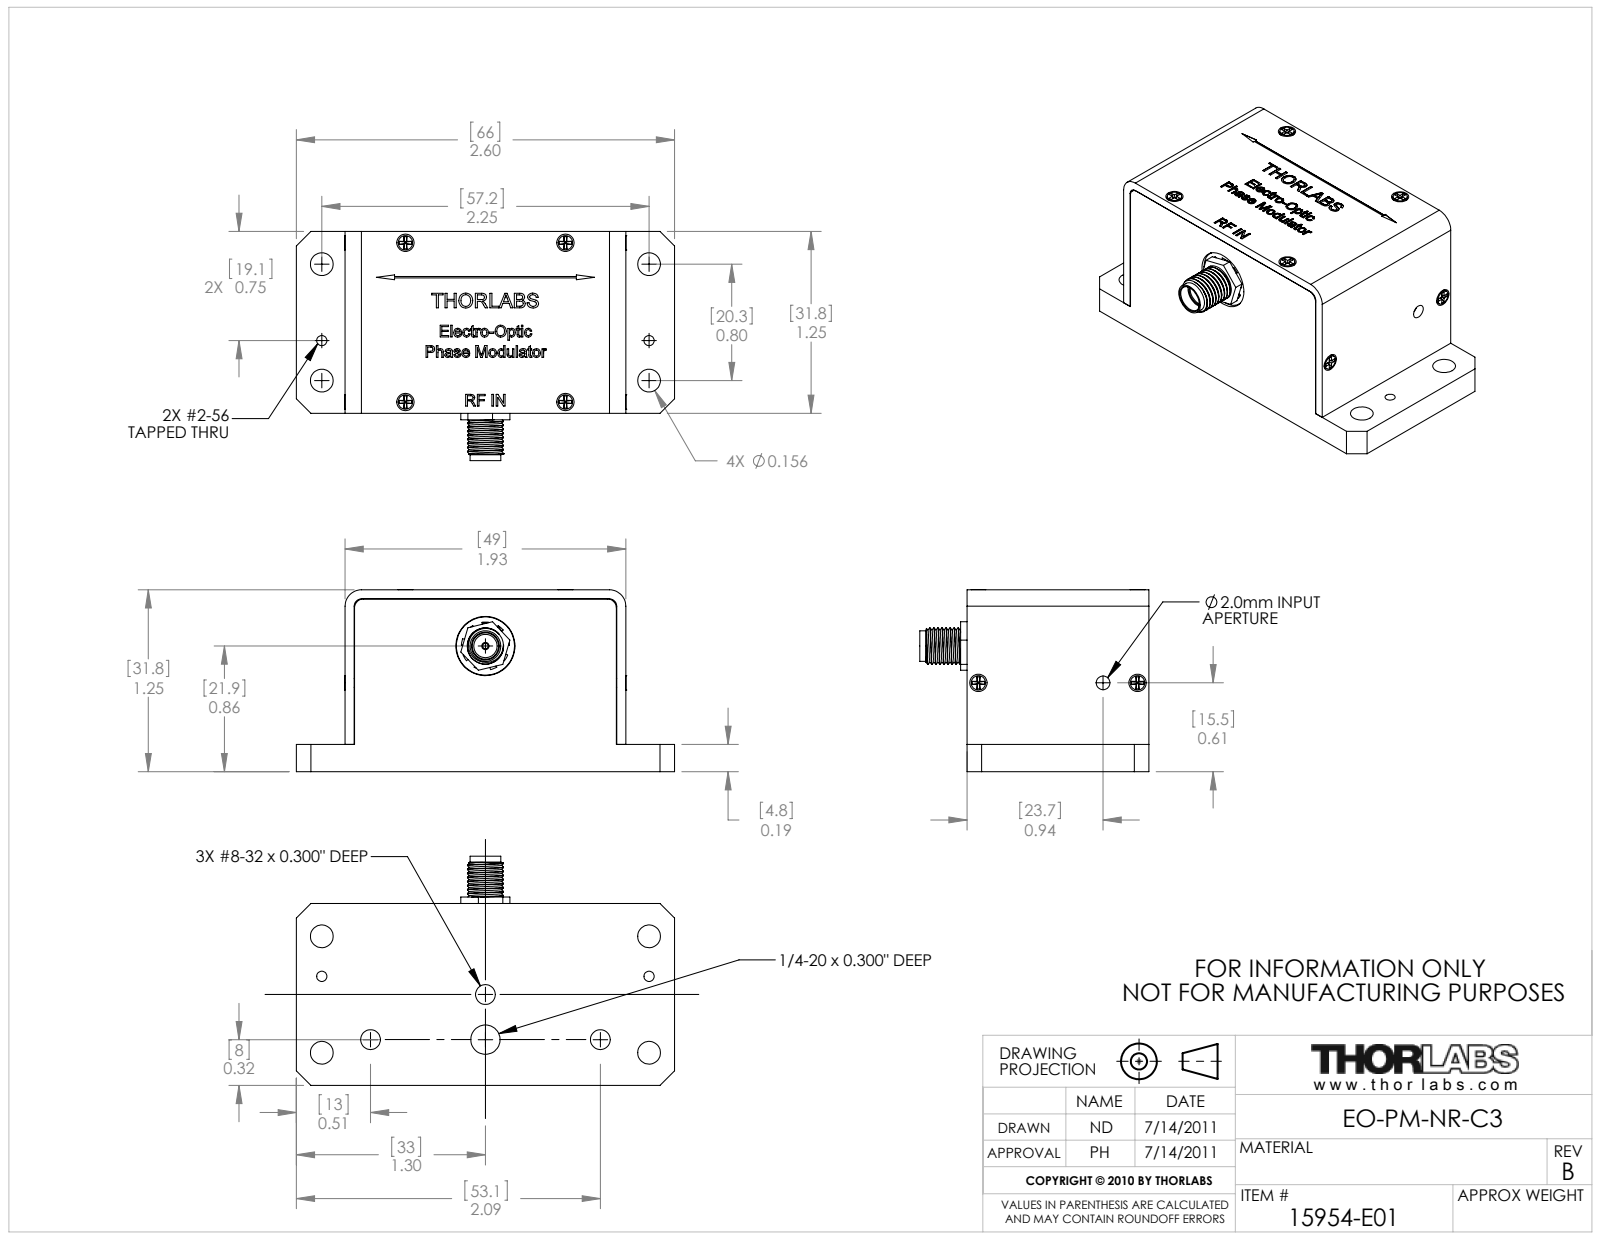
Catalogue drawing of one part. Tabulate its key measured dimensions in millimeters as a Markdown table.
| quantity | value |
| --- | --- |
| part name | 15954-E01 |
| STEP written by | SolidWorks 2011 (AUTOMOTIVE_DESIGN) |
| units | millimeters |
| bodies | 13 solids, 997 faces (529 planar, 171 cylindrical, 297 other) |
| overall size | 66.04 × 40.01 × 31.79 |
| volume | 28 528 mm³ |
| surface area | 18 673 mm² |
| round holes (diameter × count) | 1.78 × 8, 1.19 × 6, 3.97 × 4, 3.45 × 3, 0.94 × 1, 1.27 × 1, 2.38 × 1, 4.06 × 1, 4.19 × 1, 4.6 × 1, 5.11 × 1, 6.35 × 1 |
| round bosses / shafts (diameter × count) | 2.51 × 6, 1.52 × 6, 10.16 × 1, 8 × 1, 6.3 × 1, 5.33 × 1, 1.27 × 1 |
| partial cylindrical surfaces (radius × count) | 1.27 × 2, 1.59 × 2, 2.86 × 2, 3.17 × 2, 3.26 × 2, 3.49 × 1, 4.19 × 1 |
| main face-to-face distances | 31.76, 3.18, 28.58, 30.18, 1.59, 47.43, 25.4, 1.58, 8.89, 21.29 |
| hole center spacings | 15.08, 19.7, 28.14, 30.33, 42.71, 48.88, 27.78, 57.16 |
